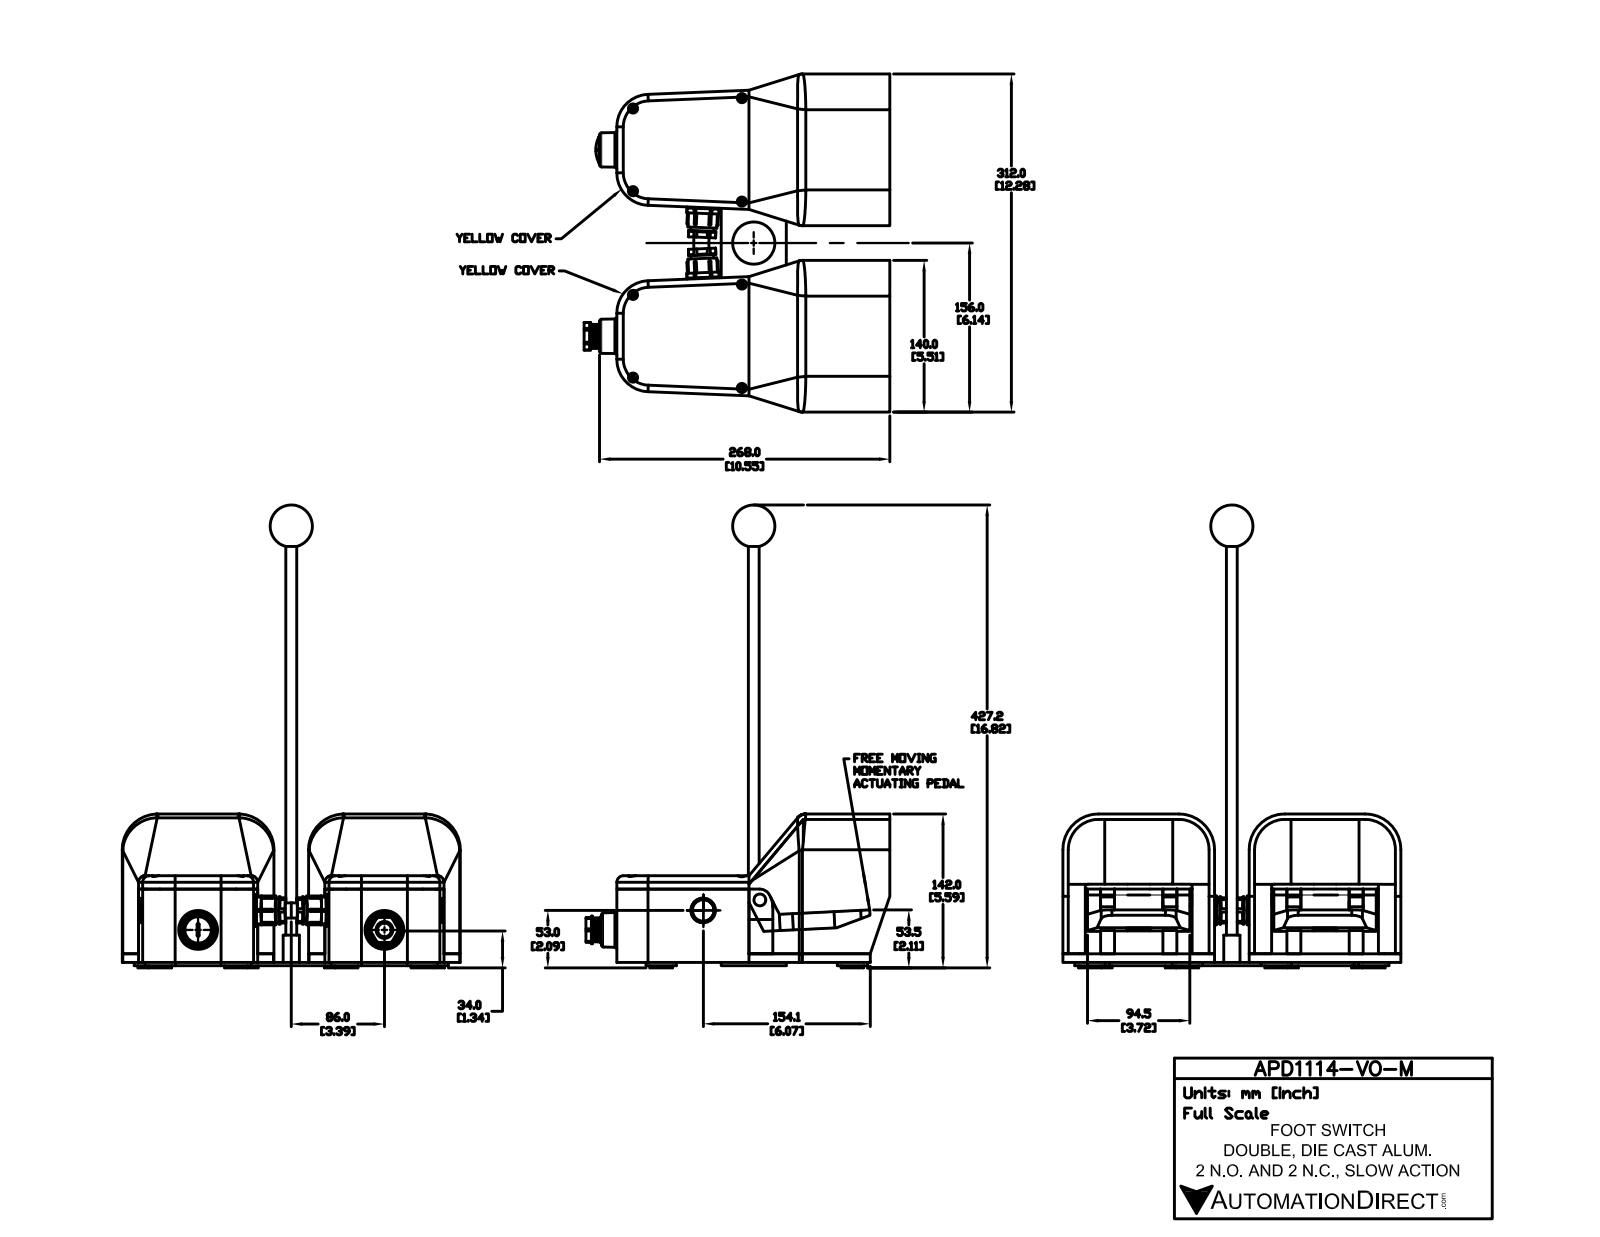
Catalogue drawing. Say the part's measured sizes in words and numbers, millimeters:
The part is named "APD1114-V0-M". Its 3-D file was written by "SolidWorks 2015 (AUTOMOTIVE_DESIGN)". It is 36 solids with 829 faces: 502 planar, 213 cylindrical and 114 other. Overall it measures 427.2 by 312 by 282.2 millimeters. Its volume is 3 215 000 cubic millimeters and its surface area 575 900 square millimeters. Round holes: 8 of diameter 8.5, 4 of diameter 22.8, 1 of diameter 12.6, 1 of diameter 15.6. Round bosses or shafts: 8 of diameter 28, 8 of diameter 21, 4 of diameter 19.9, 2 of diameter 29.7, 2 of diameter 26.7, 2 of diameter 25.2, 2 of diameter 21.5, 1 of diameter 25.5. Partial cylindrical surfaces (rounded edges, fillets, slot ends): 34 of radius 1, 12 of radius 1.1, 10 of radius 10, 5 of radius 6, 4 of radius 28, 4 of radius 30, 4 of radius 33, 1 of radius 20. The main face-to-face distances are 5, 135, 172, 8, 59.6, 140, 67.7, 59.7, 67.6, 3. The hole center spacings are 101, 132.2, 172, 76.3, 95.5, 132.4, 191, 207.6.
